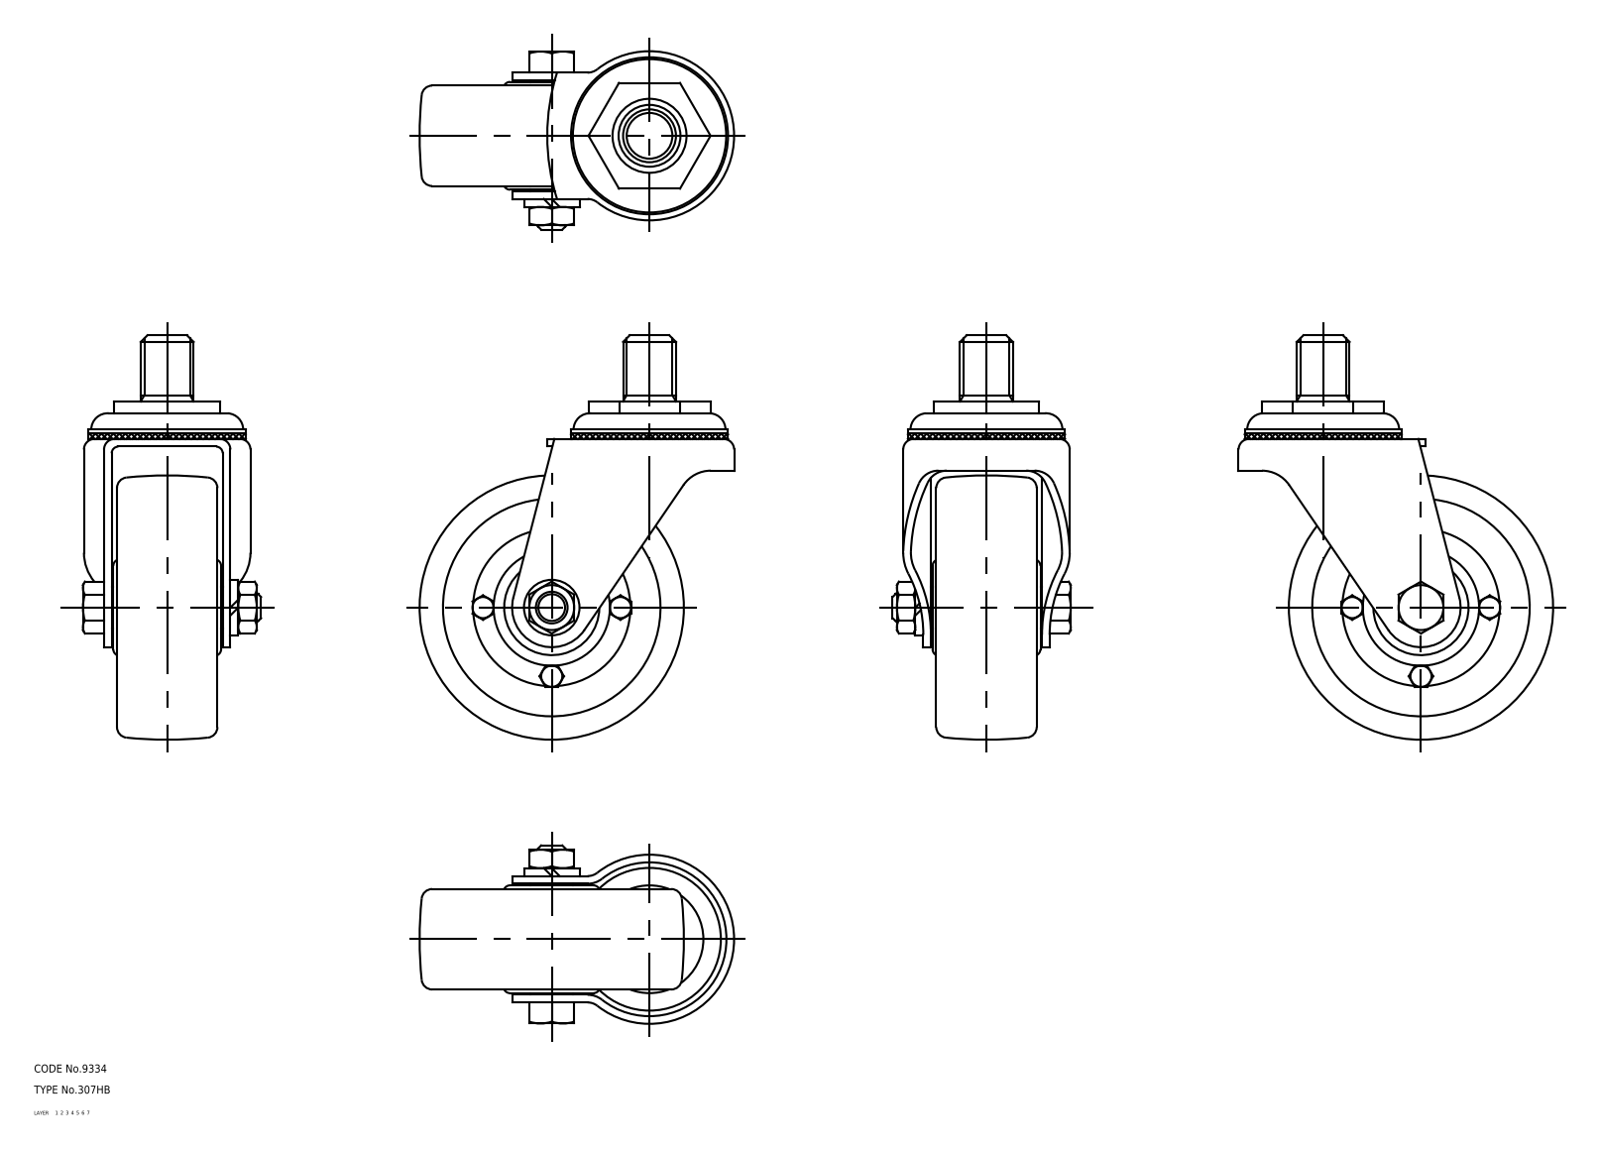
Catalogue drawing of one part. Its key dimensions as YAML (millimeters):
part_name: "67127949; 67127962; 67127975; 67127988"
step_written_by: "CADfix (AUTOMOTIVE_DESIGN)"
units: millimeters
bodies: {solids: 4, faces: 312, planar: 0, cylindrical: 0, other: 312}
overall_size: [153, 119, 67.4]
volume: 329714
surface_area: 67376
